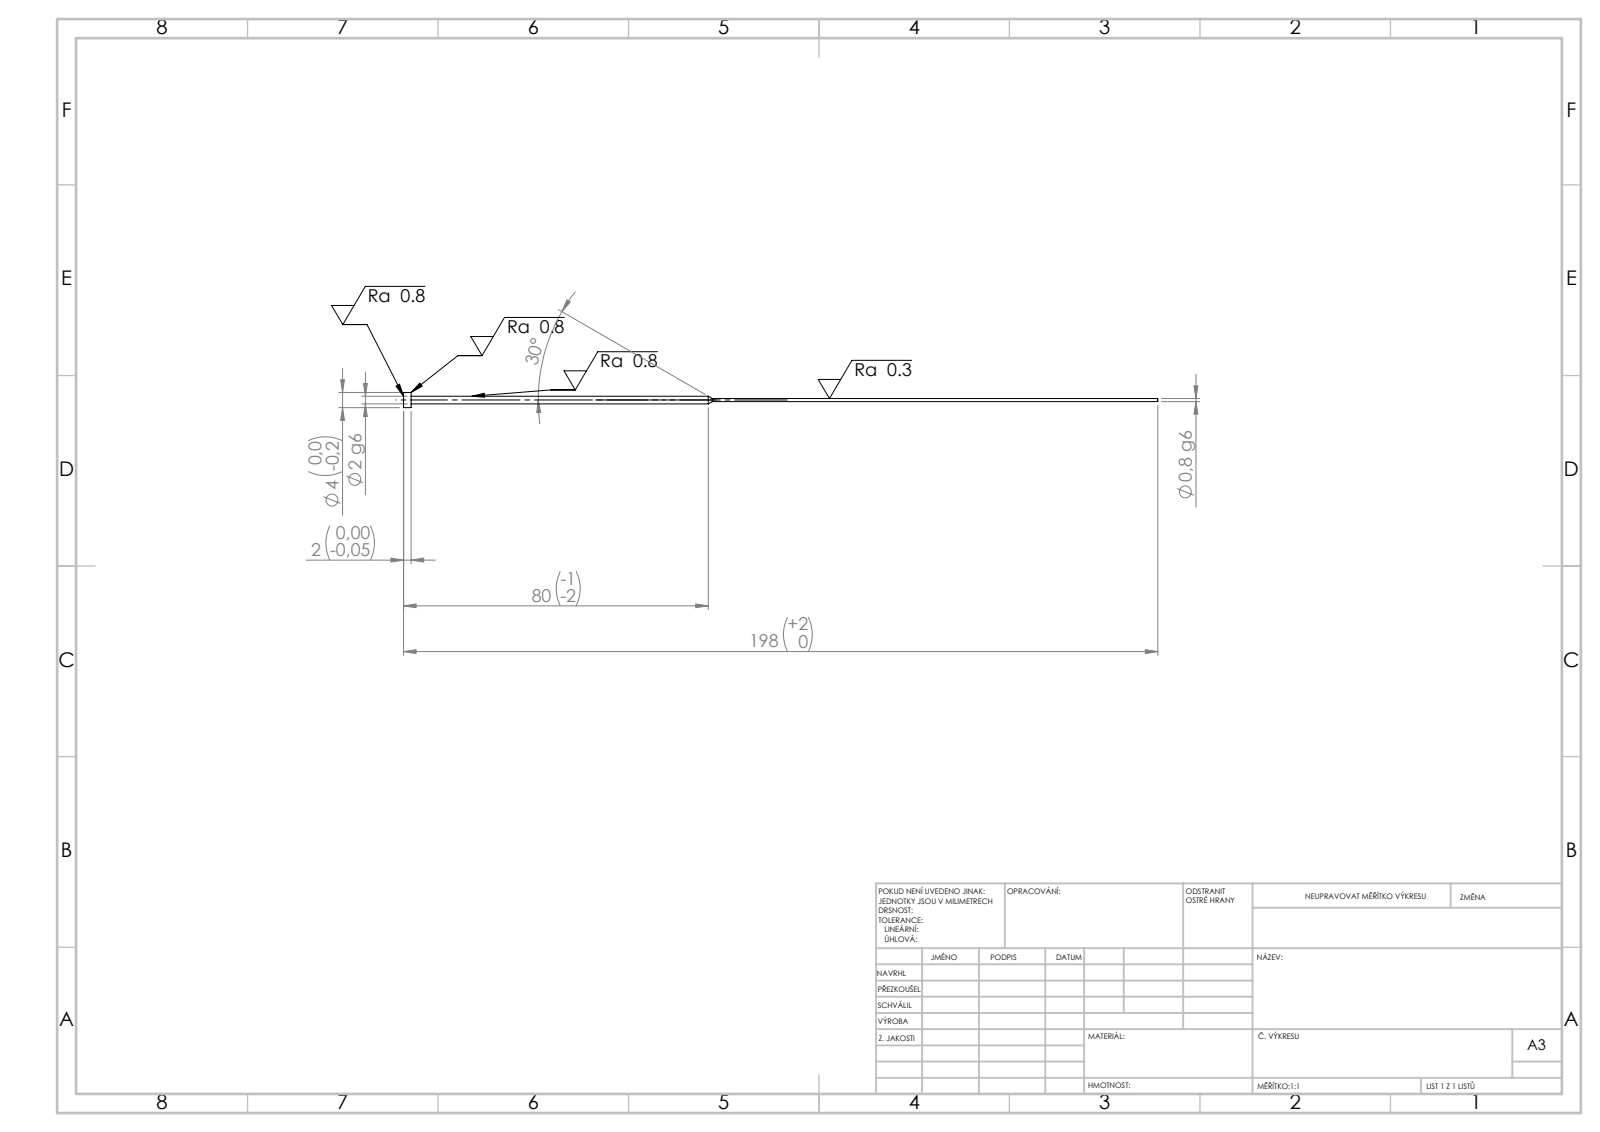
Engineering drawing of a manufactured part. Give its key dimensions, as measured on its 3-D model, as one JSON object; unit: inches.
{"step_written_by": "SolidWorks 2019 (CONFIG_CONTROL_DESIGN)", "units": "inches", "bodies": {"solids": 1, "faces": 11, "planar": 3, "cylindrical": 6, "other": 2}, "overall_size": [7.795, 0.157, 0.157], "volume_in3": 0.02, "surface_area_in2": 1.3, "round_bosses_or_shafts": [[0.157, 1], [0.079, 1], [0.031, 1]], "face_to_face_distances": [0.079, 7.717, 7.795]}
